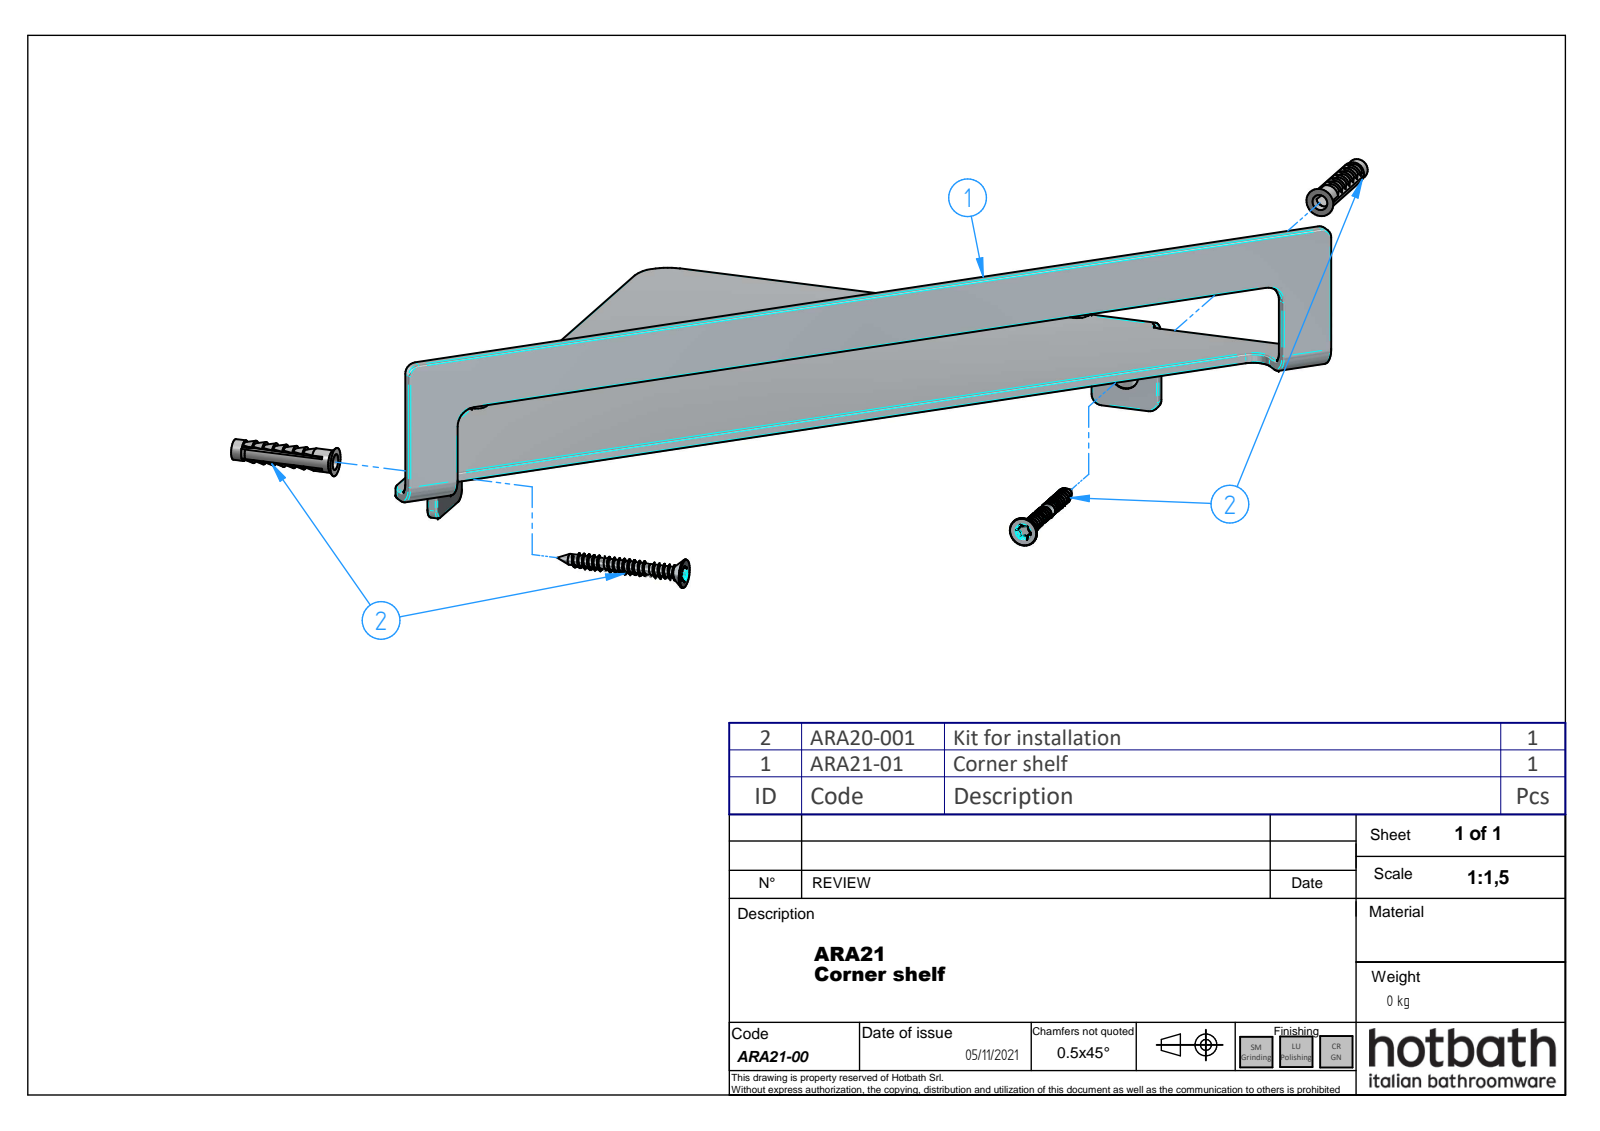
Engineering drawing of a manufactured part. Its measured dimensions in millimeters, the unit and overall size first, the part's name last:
Units: millimetres
Overall size (bounding box): 250.27 × 250.27 × 66.08
Round holes (diameter × count): ⌀5 ×2, ⌀8.2 ×2
Round bosses / shafts (diameter × count): ⌀8 ×2, ⌀3.05 ×2
Partial cylindrical surfaces — rounded edges, fillets, slot ends (radius × count): R0.5 ×38, R0.1 ×24, R3 ×13, R0.3 ×12, R0.8 ×12, R5 ×6, R6 ×3, R2.98 ×2
Main face-to-face distances: 3, 5.85, 8.85, 15, 41.79, 38.79, 14, 11, 26.79, 23.79
Volume: 76 324 mm³ · Surface area: 55 793 mm²
Bodies: 3 solids, 436 faces (55 planar, 167 cylindrical, 214 other)
Part name (STEP PRODUCT): ARA21-00; ARA21-01; ARA20-001_oa_0; C092090 (+1 more)
STEP written by: ST-DEVELOPER v16.7 (AP242_MANAGED_MODEL_BASED_3D_ENGINEERING_MIM_LF)
